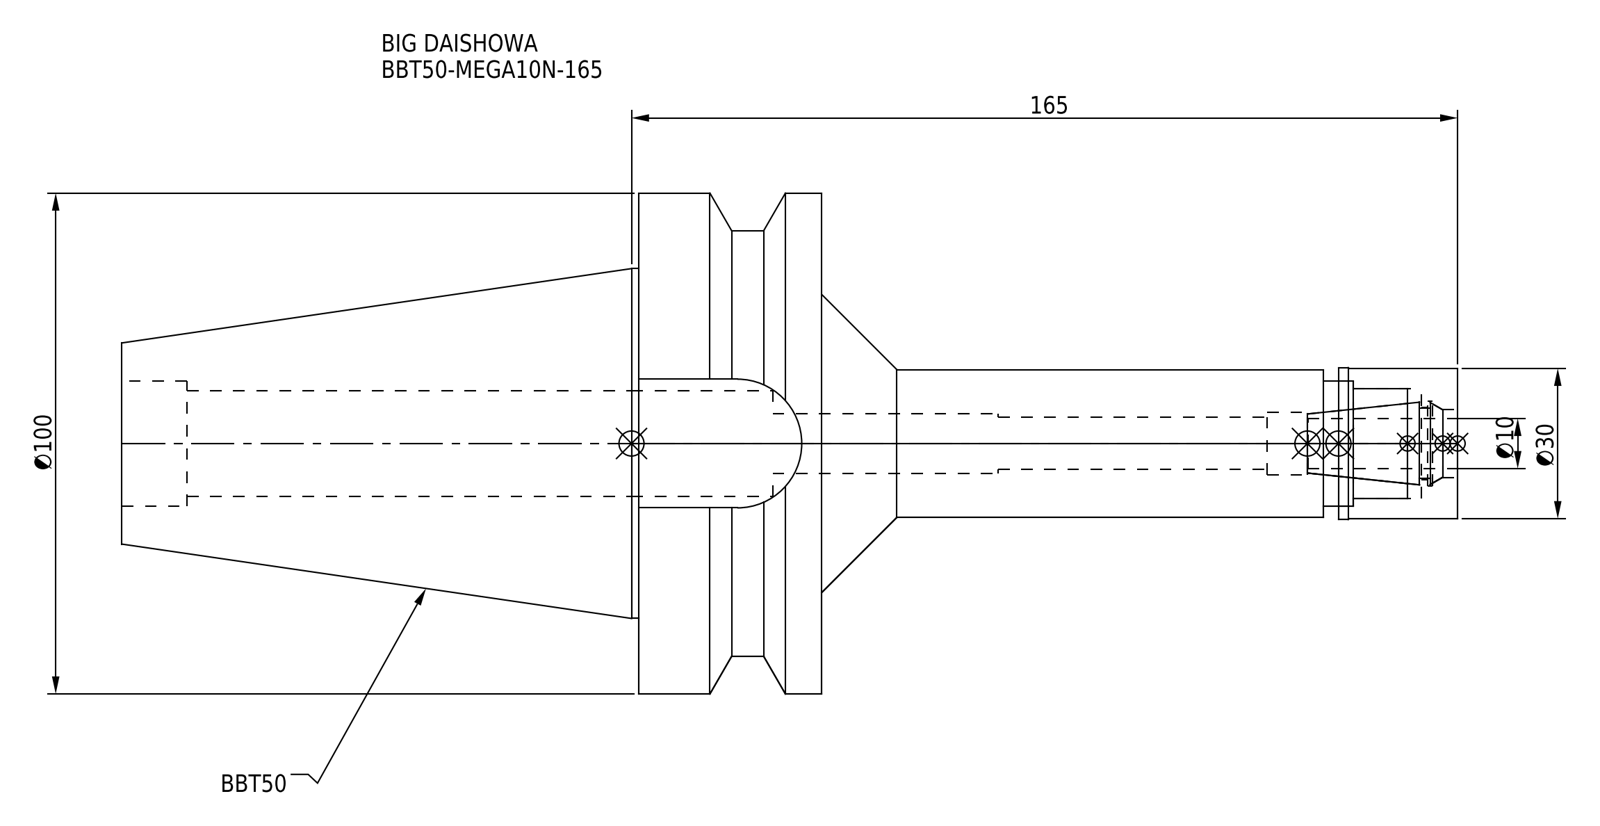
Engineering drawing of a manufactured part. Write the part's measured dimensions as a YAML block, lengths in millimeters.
part_name: "DXF_TEMP_ASSY_ASM_4_ASM.stp; BBT50MN10165-100_ASM.stp; BBT50-MEGA10N-165; MGN10_1.stp (+3 more)"
step_written_by: "SolidWorks 2019 (CONFIG_CONTROL_DESIGN)"
units: millimeters
bodies: {solids: 2, faces: 79, planar: 23, cylindrical: 42, other: 14}
overall_size: [266.8, 100, 100]
volume: 536138
surface_area: 73538
round_holes:
  - {diameter: 10.4, count: 1}
  - {diameter: 12, count: 1}
  - {diameter: 12.5, count: 1}
  - {diameter: 13.5, count: 1}
  - {diameter: 14.5, count: 1}
  - {diameter: 17, count: 1}
  - {diameter: 21.2, count: 1}
  - {diameter: 22, count: 1}
  - {diameter: 25, count: 1}
round_bosses_or_shafts:
  - {diameter: 100, count: 1}
  - {diameter: 85, count: 1}
  - {diameter: 69.85, count: 1}
  - {diameter: 30.3, count: 1}
  - {diameter: 30, count: 1}
  - {diameter: 29.5, count: 1}
partial_cylinders:
  - {radius: 12.85, count: 1}
face_to_face_distances: [36.5, 139.8, 103.3, 70.8, 127, 163.5, 266.8, 25.7, 117, 126.8]
